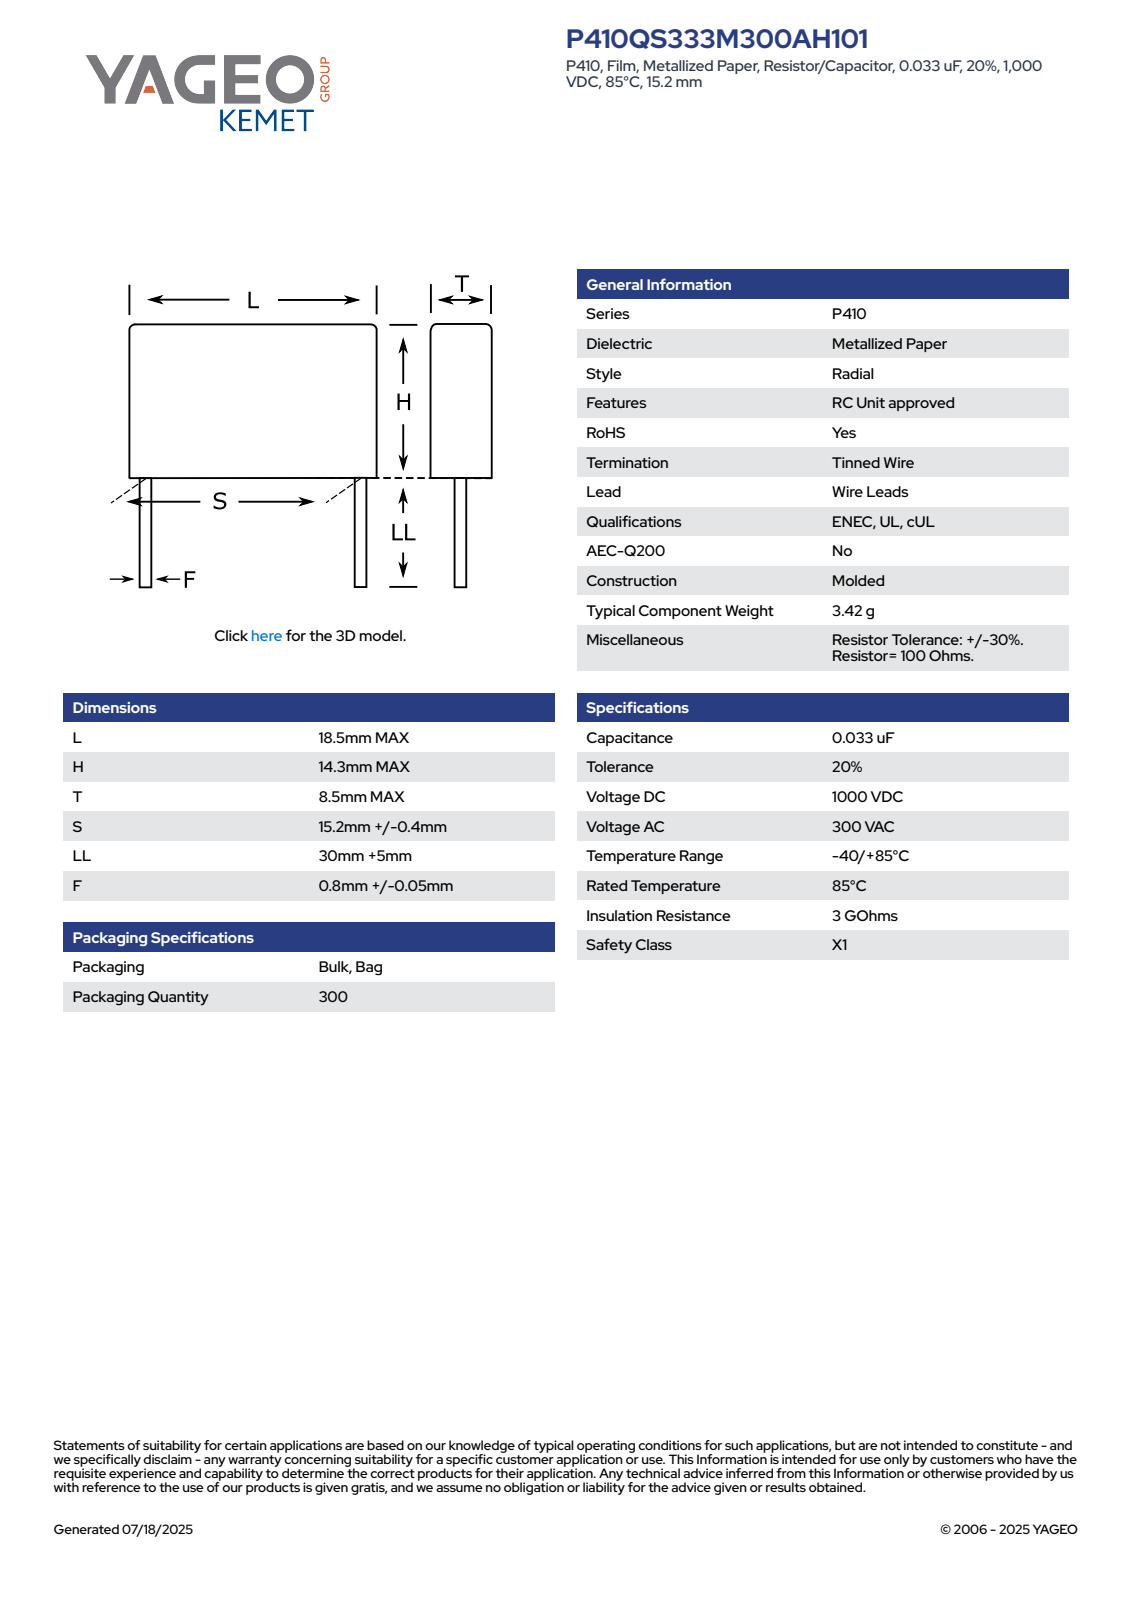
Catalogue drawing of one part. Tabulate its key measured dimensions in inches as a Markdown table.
| quantity | value |
| --- | --- |
| part name | CFR_MOLDED_18.5X14.3X8.5_L18.5H14.3T8.5S15.2LL35F0.85 |
| STEP written by | SolidWorks 2014 (AUTOMOTIVE_DESIGN) |
| units | inches |
| bodies | 4 solids, 73 faces (65 planar, 8 cylindrical, 0 other) |
| overall size | 1.941 × 0.728 × 0.335 |
| volume | 0.14 in³ |
| surface area | 1.981 in² |
| round bosses / shafts (diameter × count) | 0.033 × 2 |
| partial cylindrical surfaces (radius × count) | 0.02 × 4 |
| main face-to-face distances | 0.335, 0.563, 0.728, 0.335, 1.378, 1.941, 1.679, 0.301, 0.262, 1.614 |
